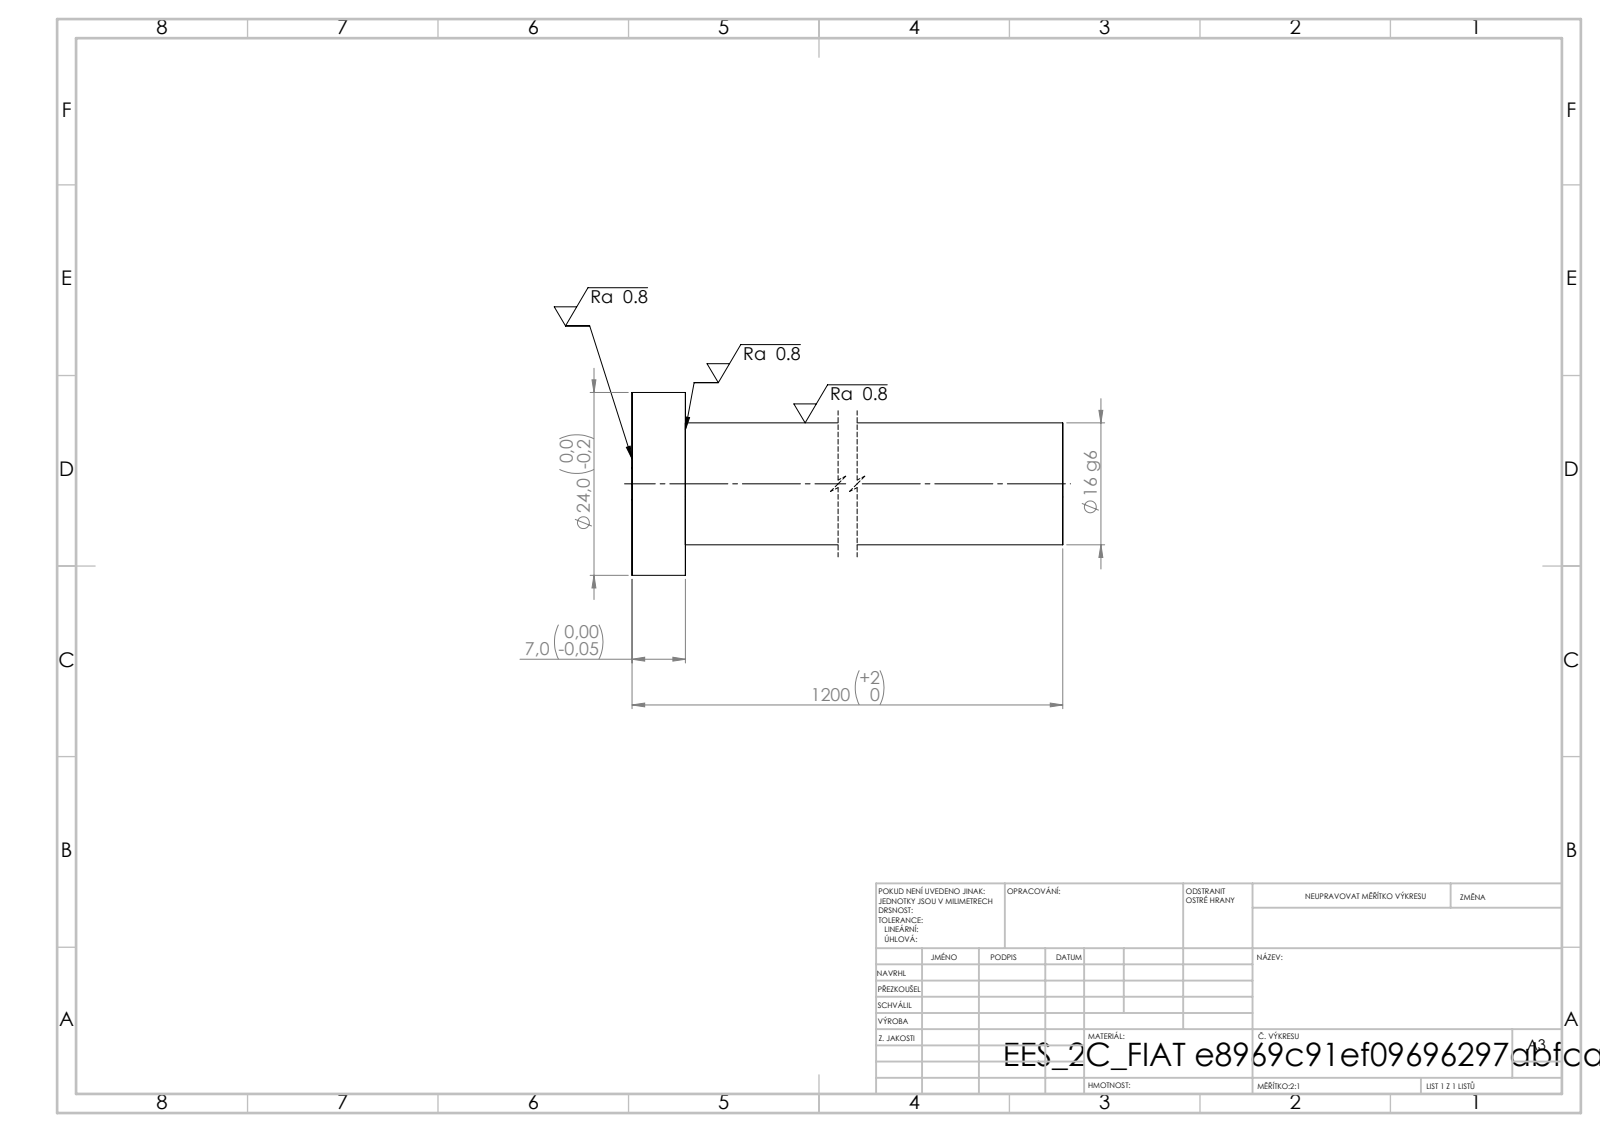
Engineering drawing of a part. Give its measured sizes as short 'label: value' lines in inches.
written by: SolidWorks 2019 (CONFIG_CONTROL_DESIGN)
unit: in
bodies: 1 solid, 7 faces (3 planar, 4 cylindrical, 0 other)
size: 47.244 × 0.945 × 0.945
volume: 14.83 in³; area: 95.17 in²
bosses: 1× ⌀0.945, 1× ⌀0.63
face distances: 0.276, 47.244, 46.969
